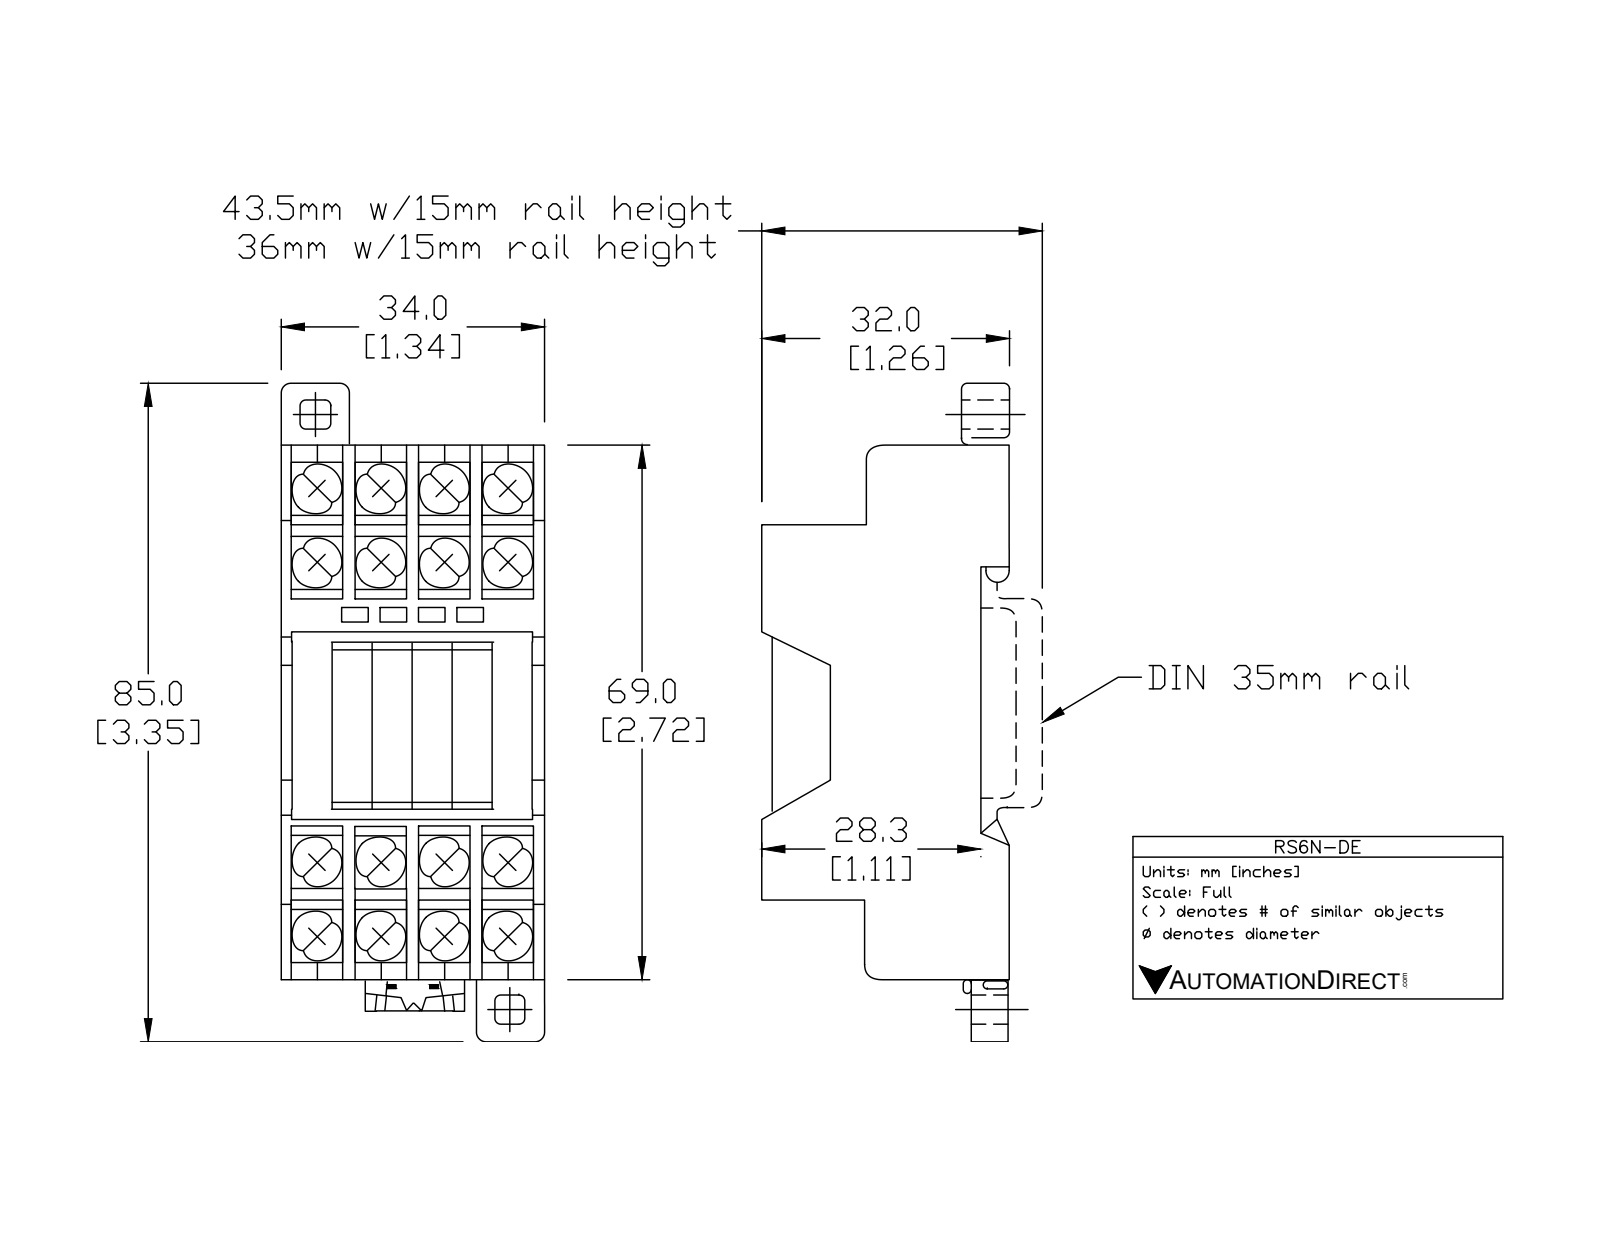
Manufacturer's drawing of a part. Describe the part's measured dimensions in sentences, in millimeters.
The part is named "RS6N-DE". Its 3-D file was written by "SolidWorks 2013 (AUTOMOTIVE_DESIGN)". It is 1 solid with 617 faces: 530 planar, 55 cylindrical and 32 other. Overall it measures 84.8 by 34 by 32 millimeters. Its volume is 49 590 cubic millimeters and its surface area 20 970 square millimeters. Round bosses or shafts: 8 of diameter 6.1, 8 of diameter 6. Partial cylindrical surfaces (rounded edges, fillets, slot ends): 8 of radius 0.8, 4 of radius 1, 2 of radius 2.5, 1 of radius 1. The main face-to-face distances are 4.6, 34, 9.1, 5.1, 13.7, 18.3, 0.5, 4.1, 1.5, 9.1.
